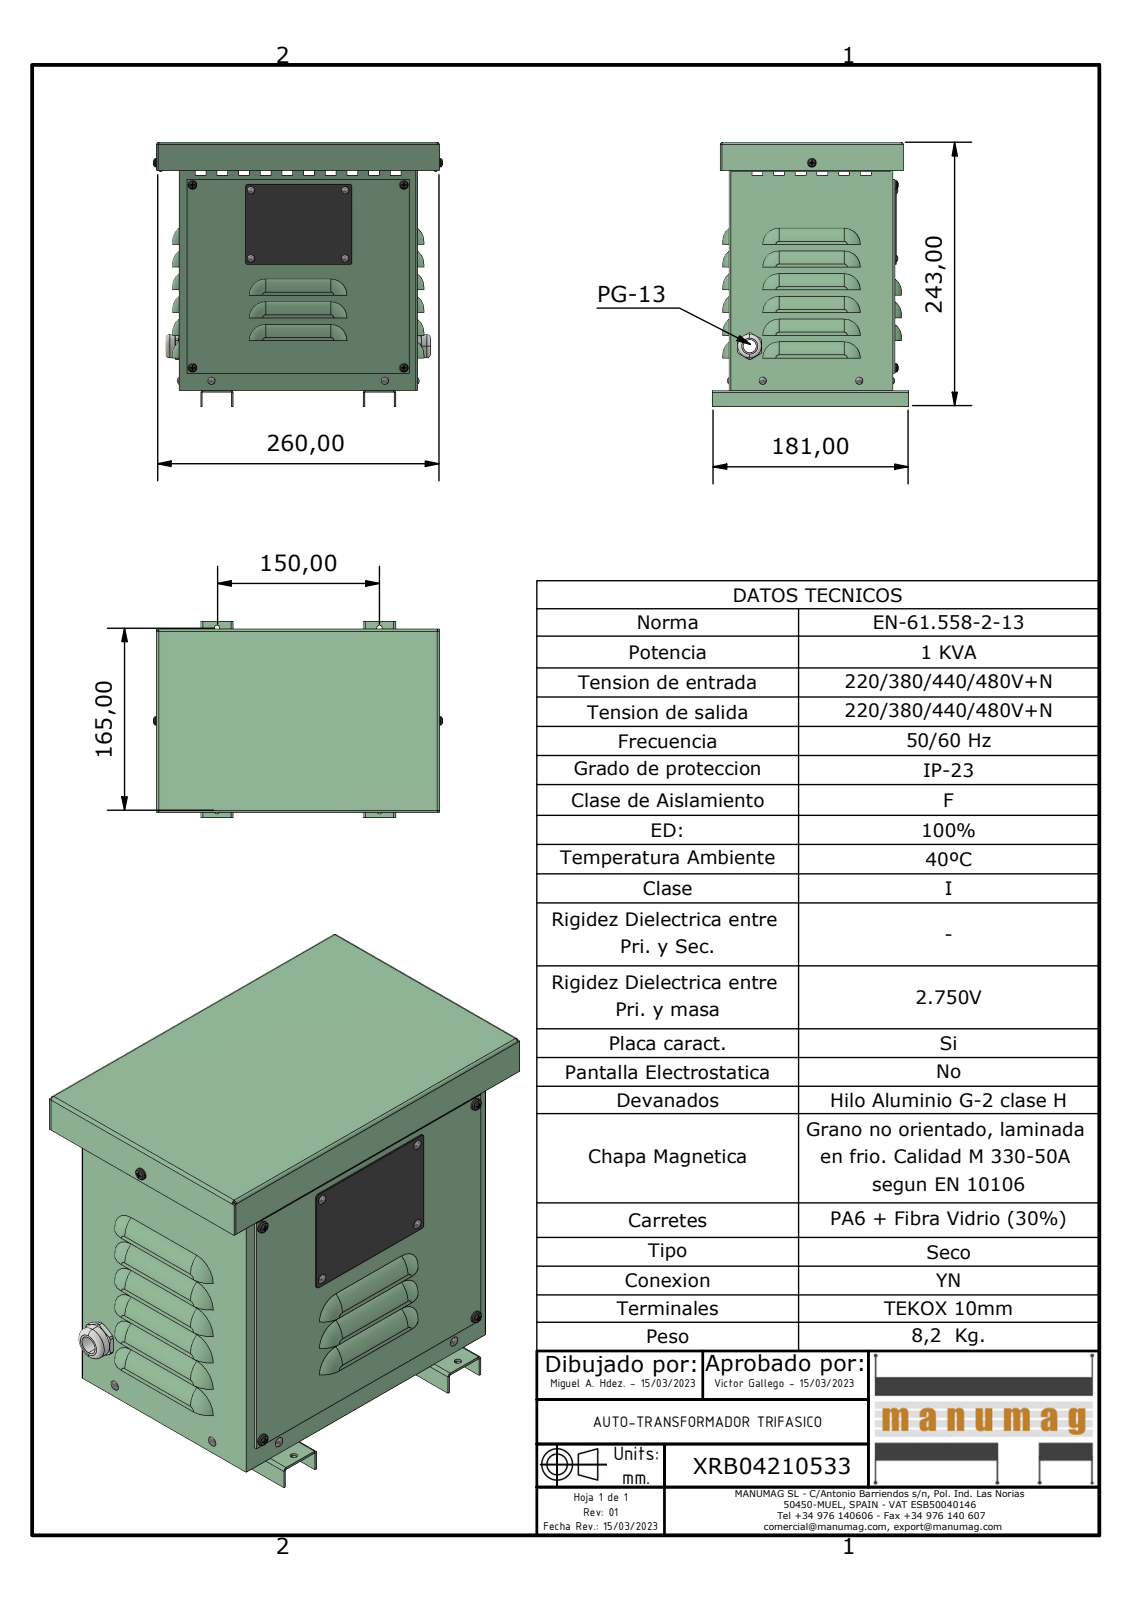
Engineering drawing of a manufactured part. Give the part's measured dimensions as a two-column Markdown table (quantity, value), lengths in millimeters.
| quantity | value |
| --- | --- |
| part name | XRB04210533; JE001 - JE002 EXPORT CUERPO; JE001 - JE002 EXPORT BASE; JE001 - JE002 EXPORT PATA (+6 more) |
| STEP written by | Autodesk Inventor 2023 (AUTOMOTIVE_DESIGN) |
| units | millimeters |
| bodies | 27 solids, 1168 faces (639 planar, 259 cylindrical, 270 other) |
| overall size | 267.13 × 244.49 × 181 |
| volume | 601 317 mm³ |
| surface area | 669 713 mm² |
| round holes (diameter × count) | 4.8 × 13, 3.8 × 5, 3 × 4, 4 × 4, 12 × 1, 22 × 1 |
| round bosses / shafts (diameter × count) | 3.2 × 8, 4 × 5, 3.62 × 5, 21.7 × 1, 20.4 × 1, 20.3 × 1, 18.95 × 1 |
| partial cylindrical surfaces (radius × count) | 14 × 24, 15 × 21, 4 × 18, 1.5 × 13, 2 × 12, 0.5 × 8, 2.5 × 8, 14.5 × 6 |
| main face-to-face distances | 1.5, 149.5, 227.99, 218.5, 229.49, 151.5, 151, 2, 153, 217 |
| hole center spacings | 169, 150, 21.22, 26, 43.01, 50, 54.23, 63 |
